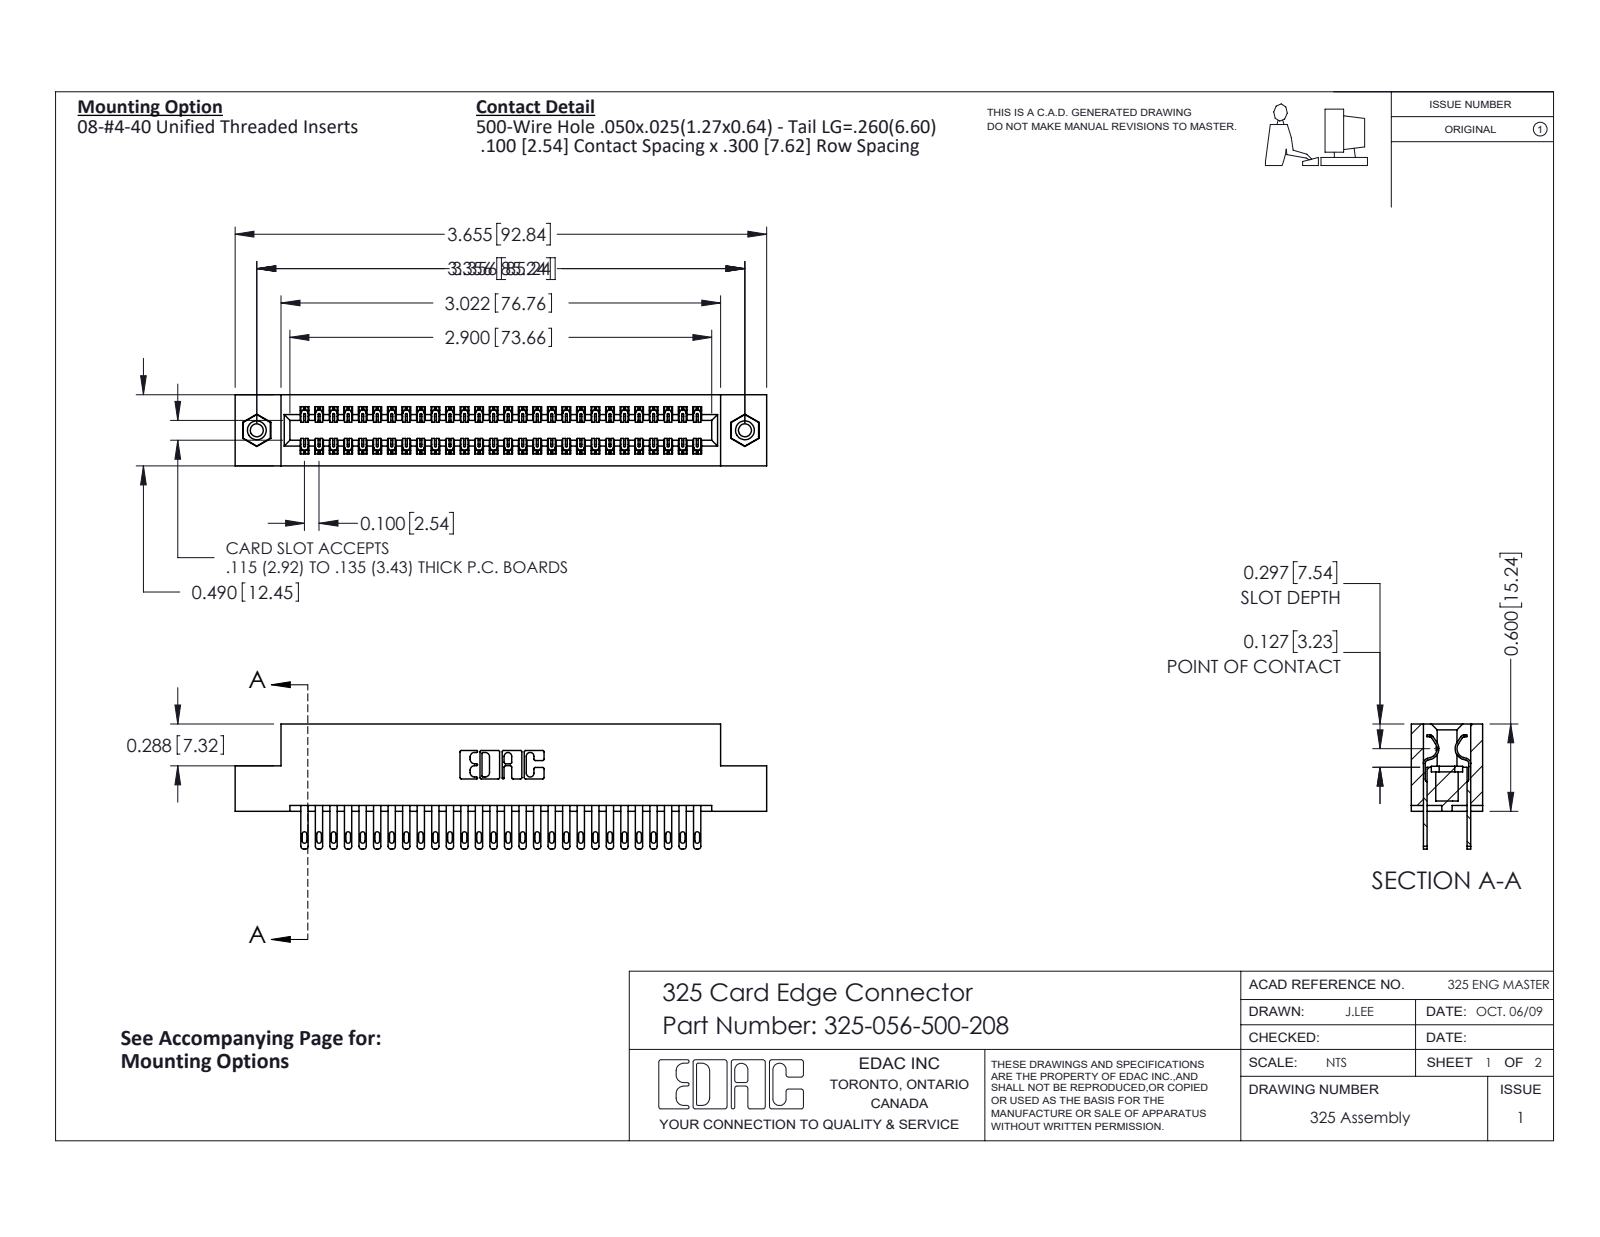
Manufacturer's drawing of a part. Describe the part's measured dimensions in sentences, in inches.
The part is named "345-250-001_345-250-003-102; 325-292-001_325-293-100; 325 Part_TI; 325-056-500-208". Its 3-D file was written by "SolidWorks 2016 (CONFIG_CONTROL_DESIGN)". It is 59 solids with 2862 faces: 1782 planar, 1064 cylindrical and 16 other. Overall it measures 3.655 by 0.86 by 0.49 inches. Its volume is 0.734 cubic inches and its surface area 22.97 square inches. Round holes: 2 of diameter 0.089, 2 of diameter 0.125, 2 of diameter 0.16. Round bosses or shafts: 2 of diameter 0.155. Partial cylindrical surfaces (rounded edges, fillets, slot ends): 84 of radius 0.006, 56 of radius 0.016, 56 of radius 0.02, 22 of radius 0.01, 6 of radius 0.007, 6 of radius 0.031, 3 of radius 0.026, 2 of radius 0.014. The main face-to-face distances are 0.083, 0.407, 0.3, 0.107, 0.383, 0.025, 0.49, 0.325, 0.275, 0.04. The hole center spacings are 3.356.
